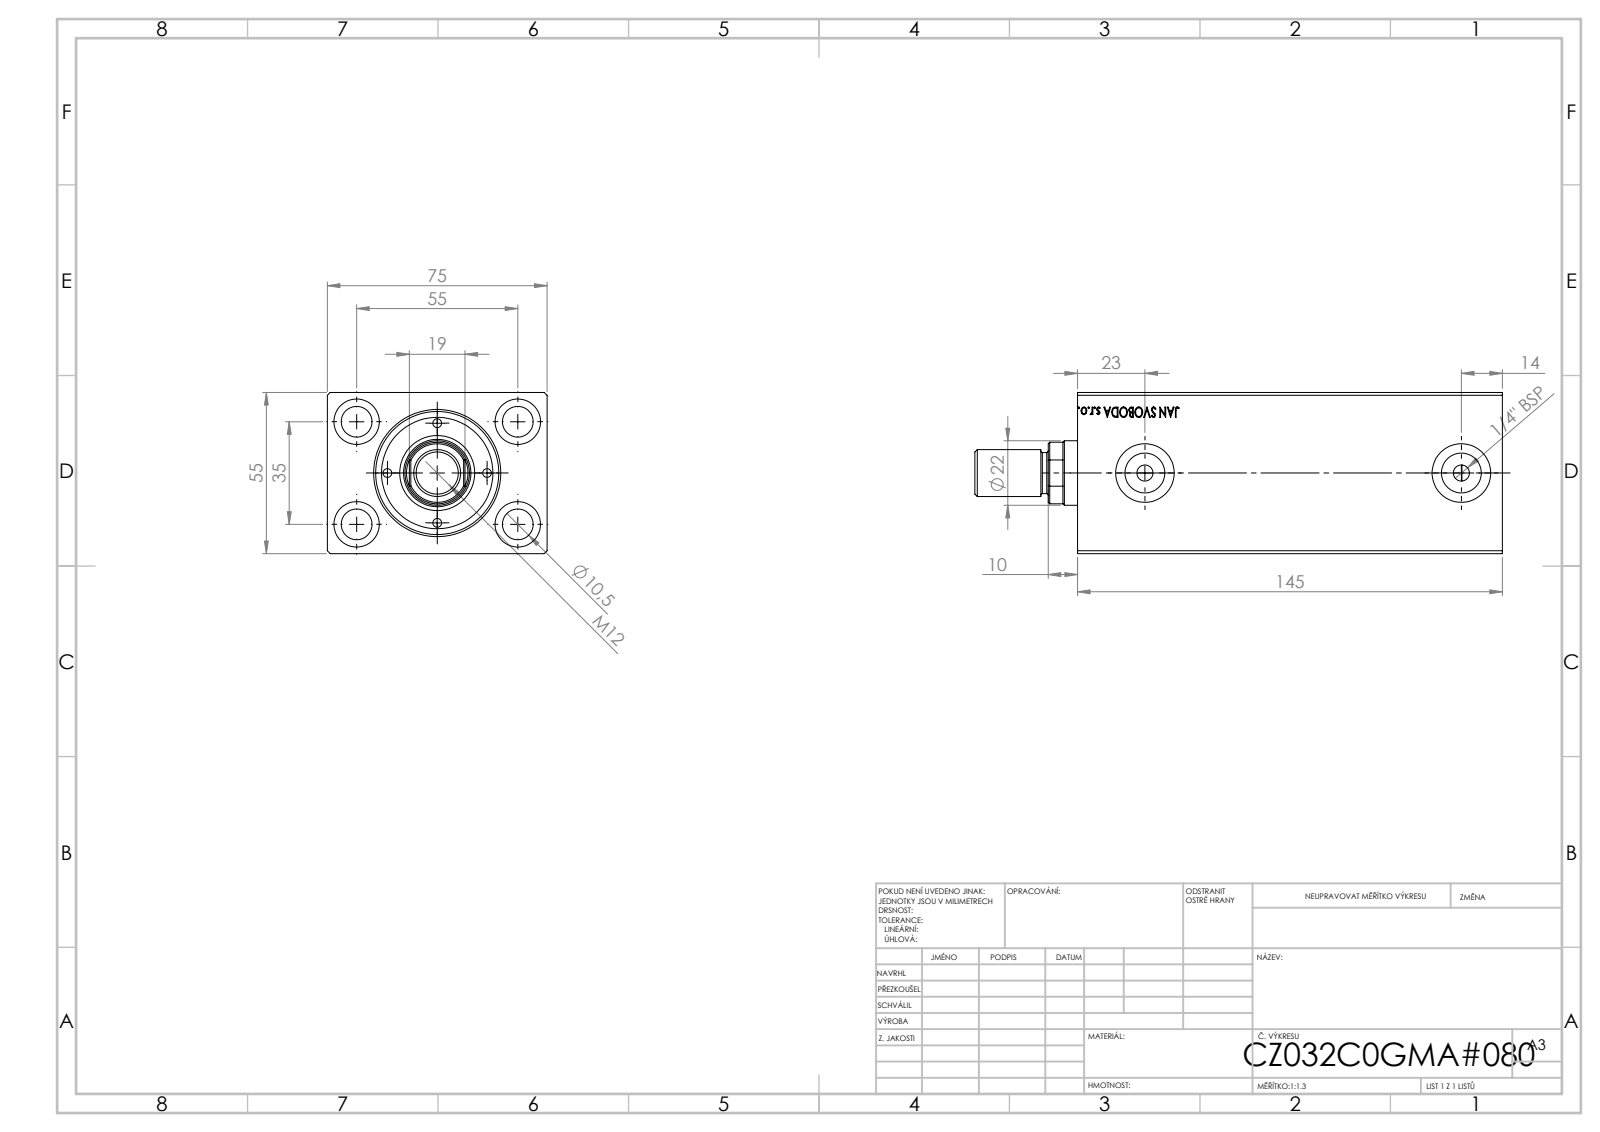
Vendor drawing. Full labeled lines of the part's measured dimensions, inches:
STEP written by: SolidWorks 2019 (CONFIG_CONTROL_DESIGN)
Units: inches
Bodies: 1 solid, 824 faces (396 planar, 46 cylindrical, 382 other)
Overall size (bounding box): 5.709 × 2.953 × 2.165
Volume: 25.83 in³ · Surface area: 124.5 in²
Round holes (diameter × count): ⌀0.413 ×4, ⌀0.61 ×4, ⌀0.217 ×2, ⌀0.315 ×2, ⌀0.535 ×2, ⌀0.787 ×2, ⌀1.26 ×1, ⌀1.417 ×1, ⌀1.654 ×1
Main face-to-face distances: 2.165, 2.953, 5.709, 5.701, 0.407, 5.302, 5.165, 0.535, 0.543, 0.394
Hole centre spacings: 1.283, 1.378, 2.165, 2.567, 3.465, 4.252
